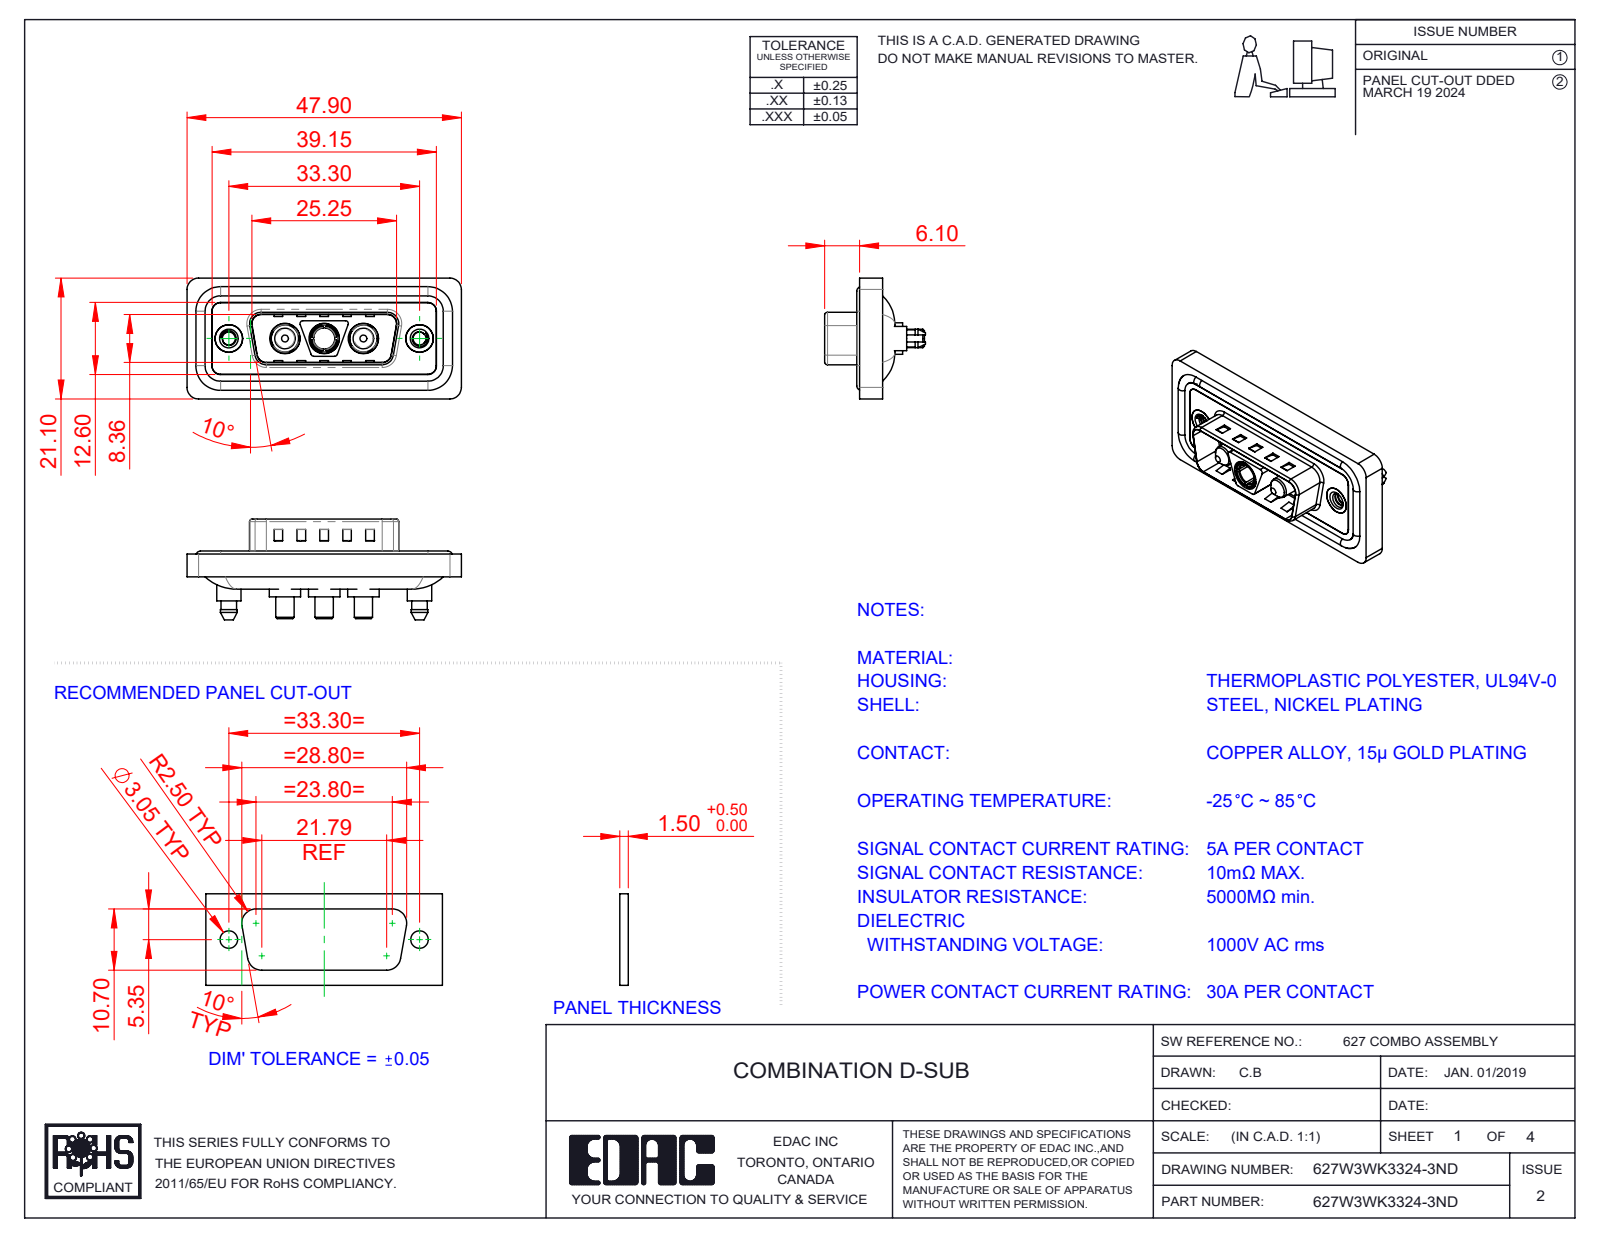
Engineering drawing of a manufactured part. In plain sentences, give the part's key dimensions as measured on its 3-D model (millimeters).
The part is named "627Combo Threaded Boardlock_5; 627Combo Threaded Boardlock_D; 627Combo Shell Front_15 Contacts; 627Combo Waterproof Housing_15 Contacts (+5 more)". Its 3-D file was written by "SolidWorks 2023 (CONFIG_CONTROL_DESIGN)". It is 13 solids with 667 faces: 247 planar, 290 cylindrical and 130 other. Overall it measures 47.9 by 21.1 by 17.6 millimeters. Its volume is 5 844 cubic millimeters and its surface area 9 477 square millimeters. Round holes: 3 of diameter 4.85, 3 of diameter 5.3, 2 of diameter 2.26, 2 of diameter 4, 2 of diameter 4.8, 2 of diameter 5, 1 of diameter 3.7. Round bosses or shafts: 4 of diameter 1.6, 3 of diameter 5.5, 3 of diameter 5.2, 3 of diameter 4.75, 3 of diameter 3.75, 3 of diameter 3.2, 2 of diameter 5.4, 2 of diameter 4.9. Partial cylindrical surfaces (rounded edges, fillets, slot ends): 28 of radius 1.5, 20 of radius 2, 12 of radius 0.5, 10 of radius 1.6, 4 of radius 0.25, 4 of radius 0.6, 4 of radius 0.65, 4 of radius 0.9. The main face-to-face distances are 0.4, 1.1, 1.5, 0.5, 3.1, 1.6, 2.9, 4, 0.7, 0.82. The hole center spacings are 6.85, 9.8, 16.65, 23.5, 13.7, 33.3.
